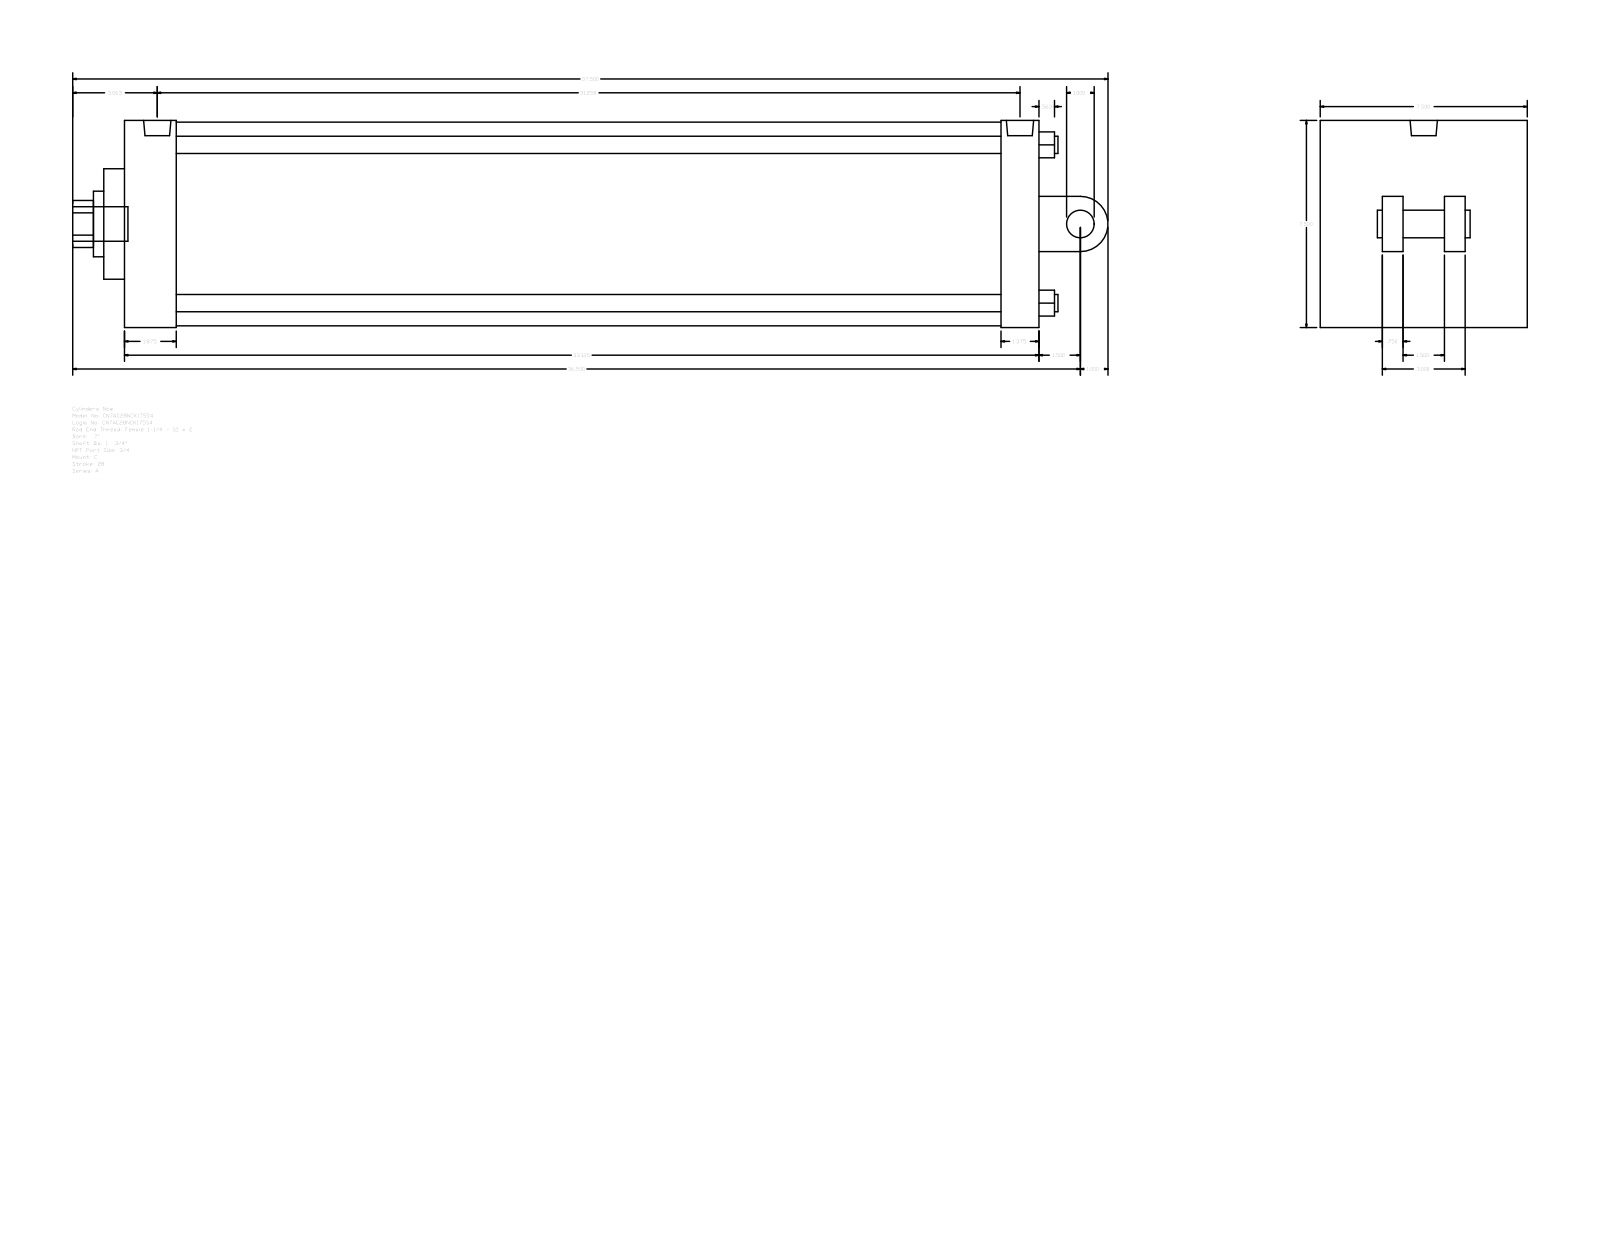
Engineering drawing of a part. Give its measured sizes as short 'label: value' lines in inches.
name: A_C__0700_1.75
written by: GSSL Pune (CONFIG_CONTROL_DESIGN)
unit: in
bodies: 0 solids, 104 faces (75 planar, 29 cylindrical, 0 other)
size: 37.5 × 7.5 × 7.5
holes: 4× ⌀0.625, 2× ⌀0.594, 1× ⌀0.989, 1× ⌀1.75, 1× ⌀2.375, 1× ⌀7.375
bosses: 2× ⌀0.594, 1× ⌀1.25, 1× ⌀1, 1× ⌀0.989
rounds: 1× R0.852, 1× R1
face distances: 7.5, 33.125, 0.75, 3, 2.25, 1.75, 1.375, 1.875, 31.25, 31.75
hole spacings: 4.052, 5.73, 8.103, 0.219
